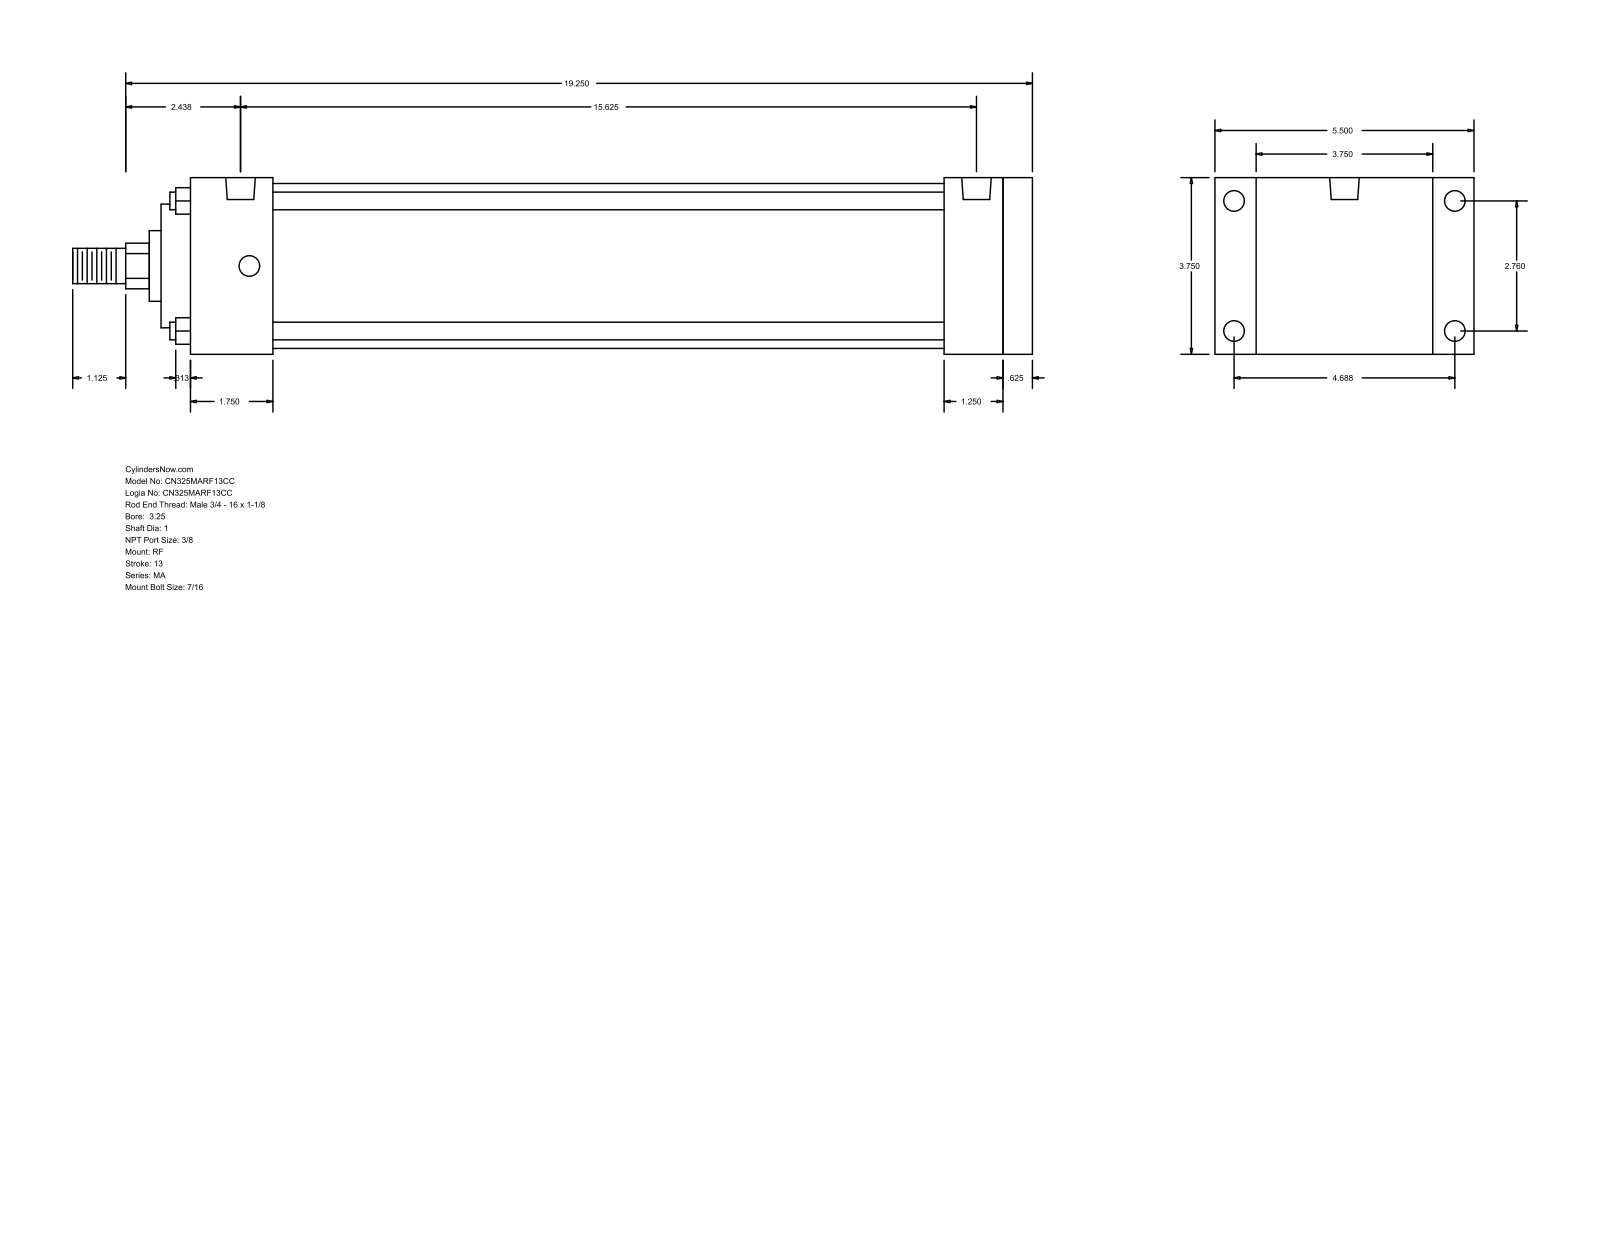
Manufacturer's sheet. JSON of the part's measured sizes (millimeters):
{"part_name": "MA_RF__0325_1", "step_written_by": "GSSL Pune (CONFIG_CONTROL_DESIGN)", "units": "millimeters", "bodies": {"solids": 0, "faces": 94, "planar": 65, "cylindrical": 29, "other": 0}, "overall_size": [517.52, 139.7, 95.25], "round_holes": [[11.11, 8], [15.93, 2]], "round_bosses_or_shafts": [[9.53, 4], [88.9, 1], [66.67, 1], [38.1, 1], [25.4, 1], [19.05, 1]], "partial_cylinders_radius": [[12.29, 1]], "face_to_face_distances": [95.24, 454.03, 438.15, 15.88, 22.23, 117.47, 406.4, 31.75, 47.63, 44.46], "hole_center_spacings": [70.1, 119.06, 138.16, 387.35, 4.76, 4.77, 392.11, 392.12]}
